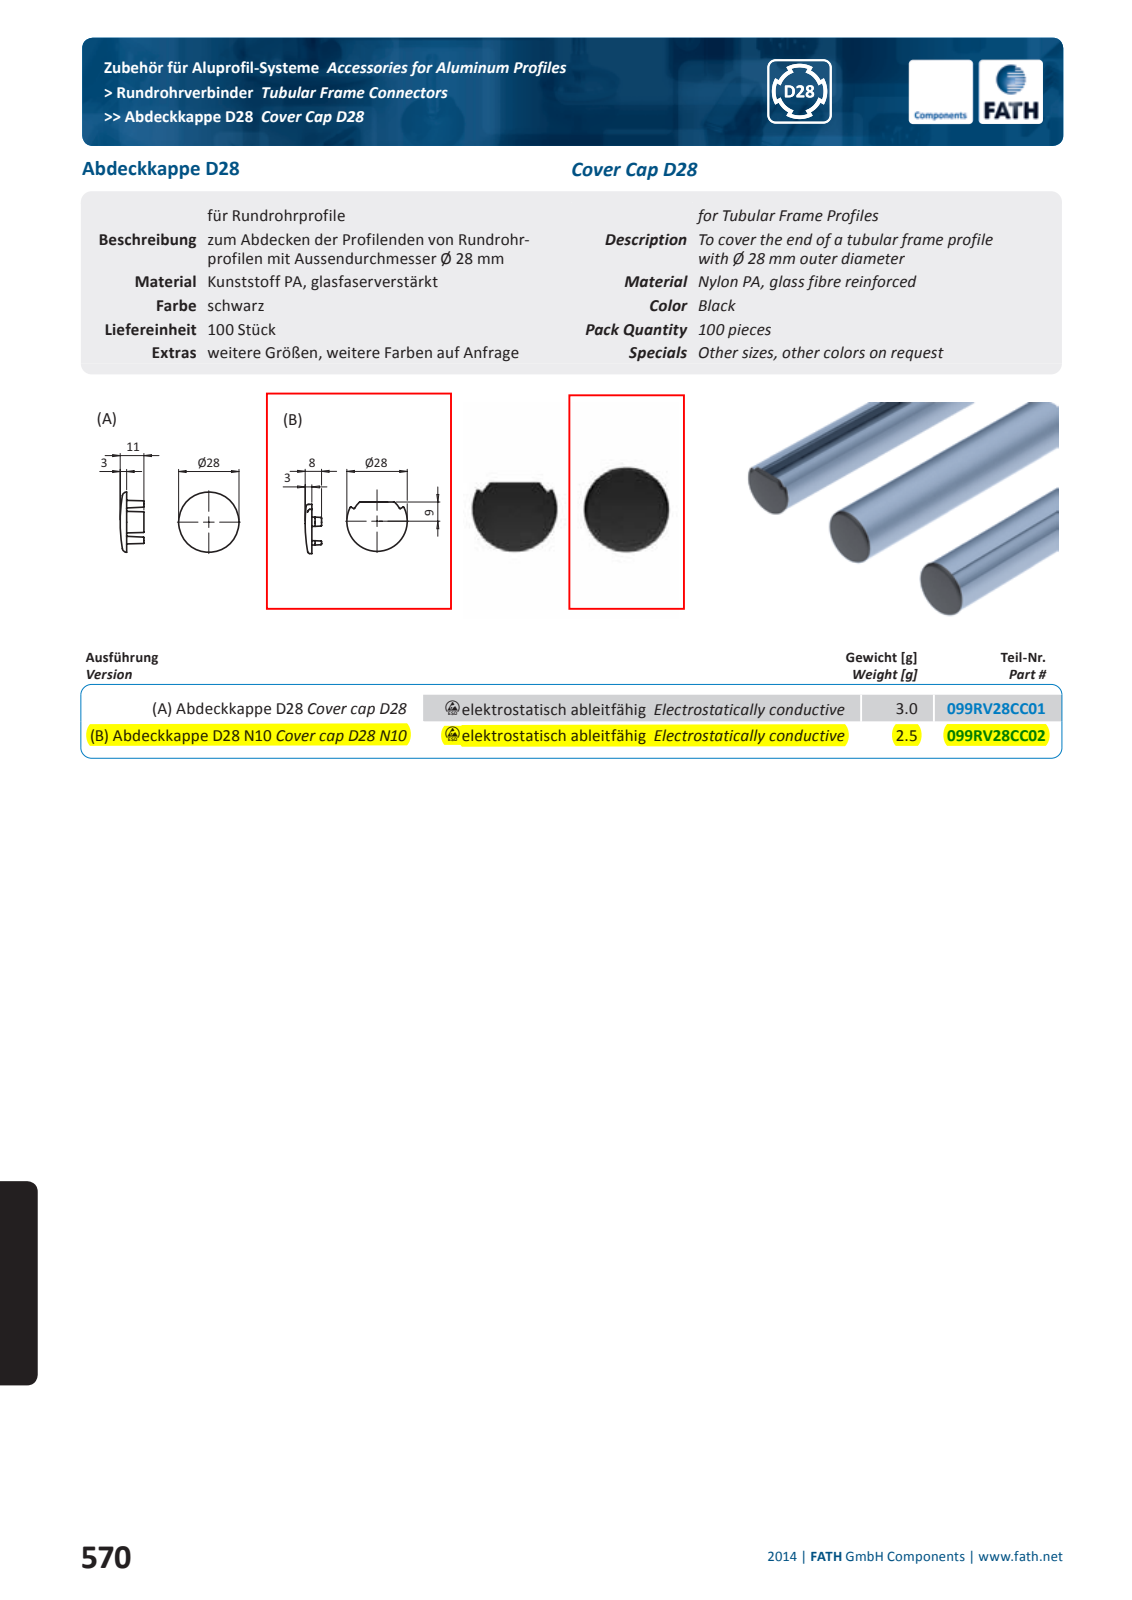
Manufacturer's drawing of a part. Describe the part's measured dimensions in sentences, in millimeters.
The part is named "fath_099rv28cc02". Its 3-D file was written by "Spatial InterOp 3D (automotive_design)". It is 1 solid with 177 faces: 30 planar, 25 cylindrical and 122 other. Overall it measures 28 by 22.9 by 7.6 millimeters. Its volume is 989 cubic millimeters and its surface area 1 410 square millimeters. Partial cylindrical surfaces (rounded edges, fillets, slot ends): 15 of radius 0.3, 8 of radius 0.5, 1 of radius 10. The main face-to-face distances are 4.5, 17.78, 10.94, 15.3, 2.5, 17.8, 10.95, 10.14, 7.64, 1.5.
